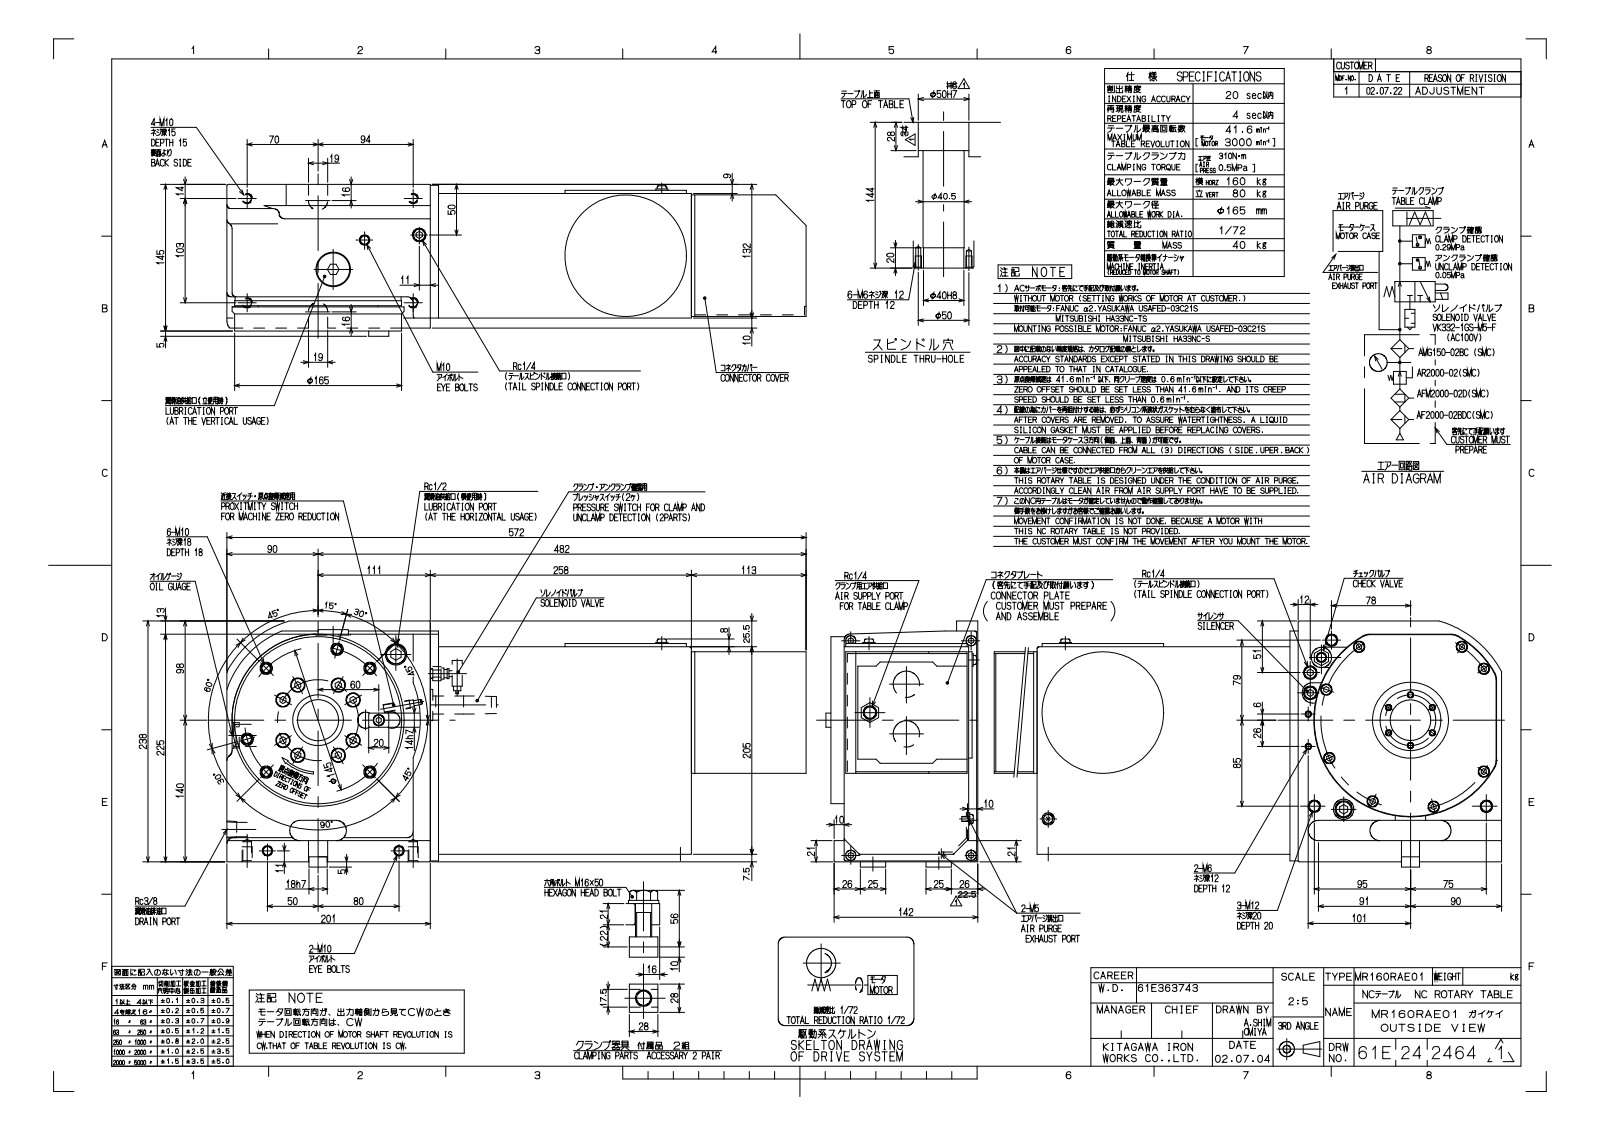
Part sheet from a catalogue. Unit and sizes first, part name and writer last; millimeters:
Units: millimetres
Overall size (bounding box): 348.7 × 269 × 257
Round holes (diameter × count): ⌀6 ×20, ⌀5 ×12, ⌀10 ×12, ⌀8.5 ×10, ⌀14 ×9, ⌀11 ×8, ⌀7 ×4, ⌀16 ×4, ⌀10.2 ×3, ⌀12 ×3, ⌀9.5 ×2, ⌀9.37 ×1
Round bosses / shafts (diameter × count): ⌀9 ×12, ⌀12 ×8, ⌀10 ×8, ⌀7 ×5, ⌀32 ×2, ⌀170 ×1, ⌀165 ×1, ⌀164 ×1
Partial cylindrical surfaces — rounded edges, fillets, slot ends (radius × count): R10 ×21, R2 ×3, R6 ×3, R7 ×2, R8.5 ×2, R3 ×1, R9 ×1, R95 ×1
Main face-to-face distances: 2.3, 118.4, 1.6, 120.7, 13, 9, 21, 131, 1, 8.3
Hole centre spacings: 25, 40, 91.42, 111.62, 35, 56.79, 35.41, 73.18
Volume: 5 825 000 mm³ · Surface area: 628 918 mm²
Bodies: 1 solid, 755 faces (506 planar, 199 cylindrical, 50 other)
Part name (STEP PRODUCT): MR160RAY07
STEP written by: ST-DEVELOPER v16.7 (AUTOMOTIVE_DESIGN)
